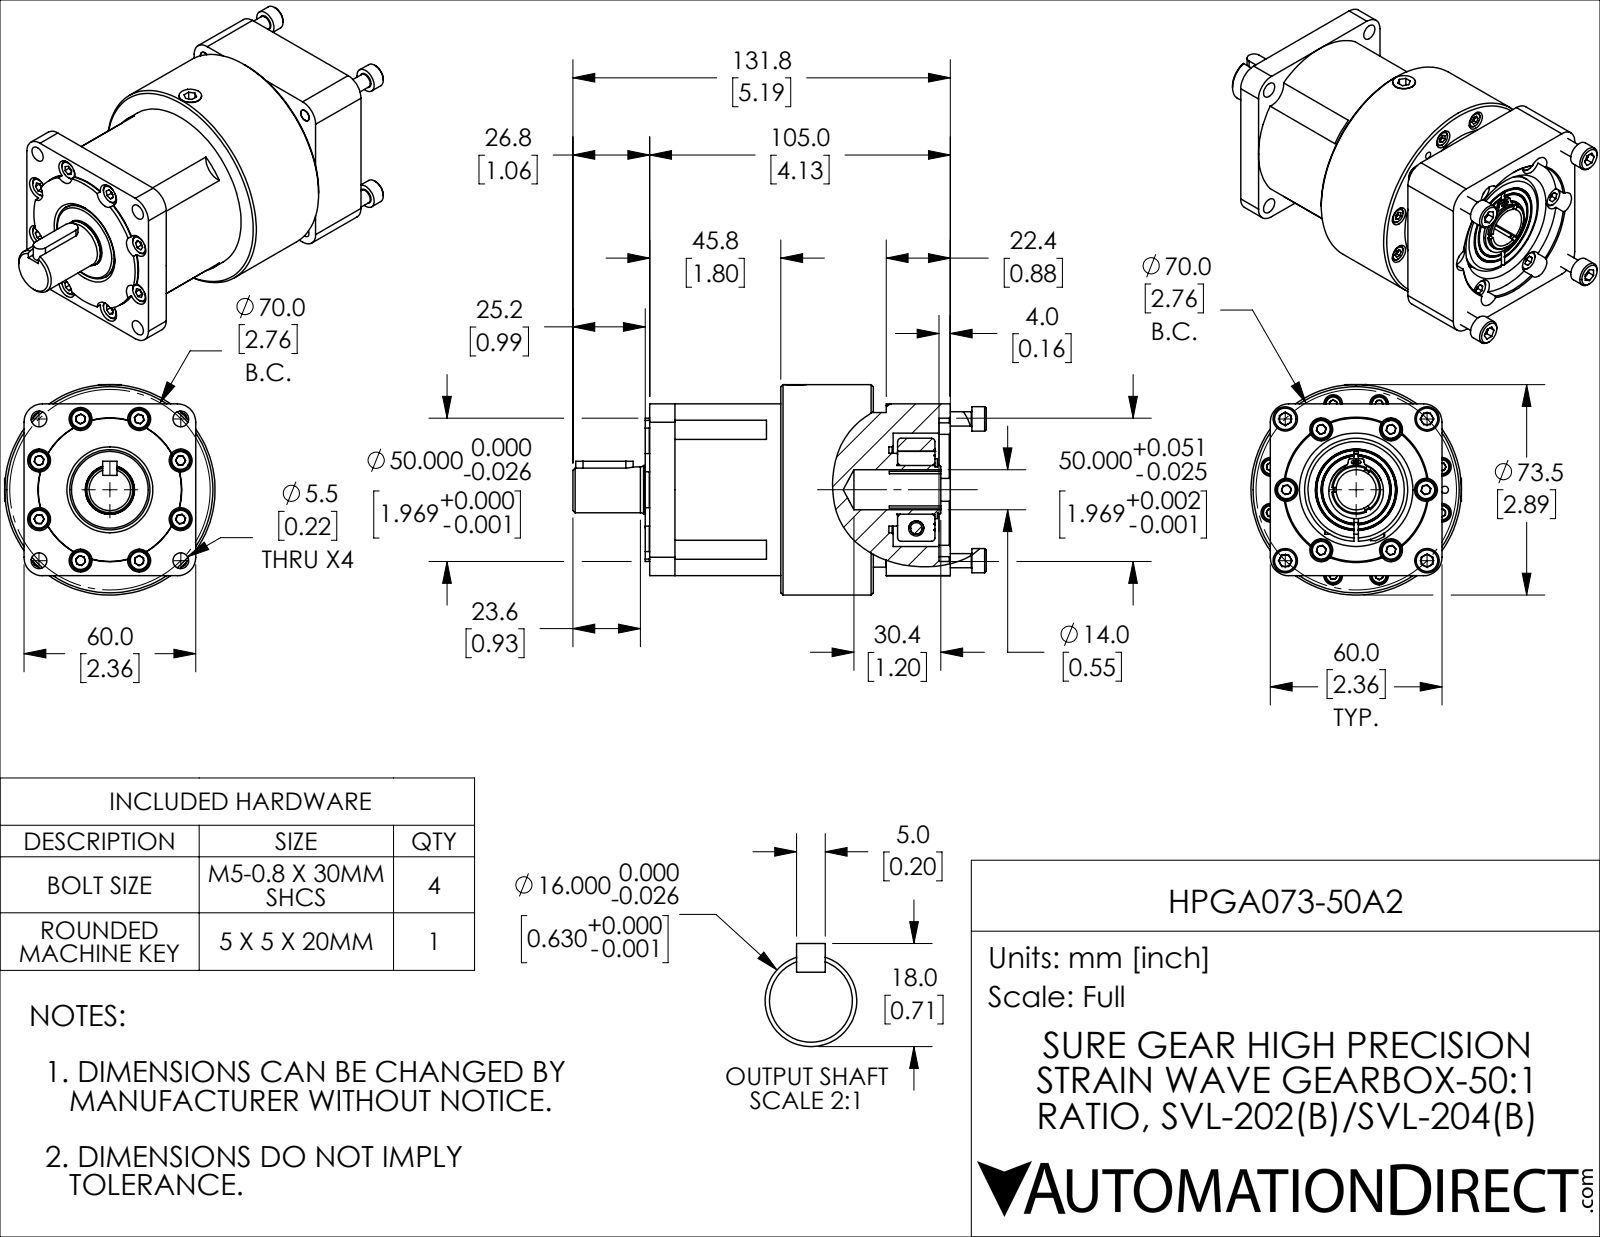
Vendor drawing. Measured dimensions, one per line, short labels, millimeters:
name: HPGA073-50A2
written by: SolidWorks 2021 (CONFIG_CONTROL_DESIGN)
unit: mm
bodies: 5 solids, 1442 faces (634 planar, 455 cylindrical, 353 other)
size: 144.3 × 73.5 × 73.5
volume: 347 100 mm³; area: 59 300 mm²
holes: 14× ⌀4.5, 14× ⌀8, 12× ⌀3.4, 12× ⌀6.5, 6× ⌀3.5, 4× ⌀4.2, 4× ⌀5.5, 3× ⌀2.5, 2× ⌀1.2, 1× ⌀4.3, 1× ⌀5.3, 1× ⌀6
bosses: 14× ⌀7, 14× ⌀4, 12× ⌀5.5, 12× ⌀3, 5× ⌀8.5, 4× ⌀5, 1× ⌀73.5, 1× ⌀60
rounds: 12× R1.2, 8× R1.7, 4× R6, 4× R6.4, 3× R25.4, 2× R0.5, 2× R1.8, 2× R2.5
face distances: 60, 106.6, 79.7, 26.9, 22.4, 84.2, 4.5, 47.3, 32.3, 36.8
hole spacings: 31, 34.1, 59.9, 9.8, 16.1, 17.5, 22.1, 33.2
